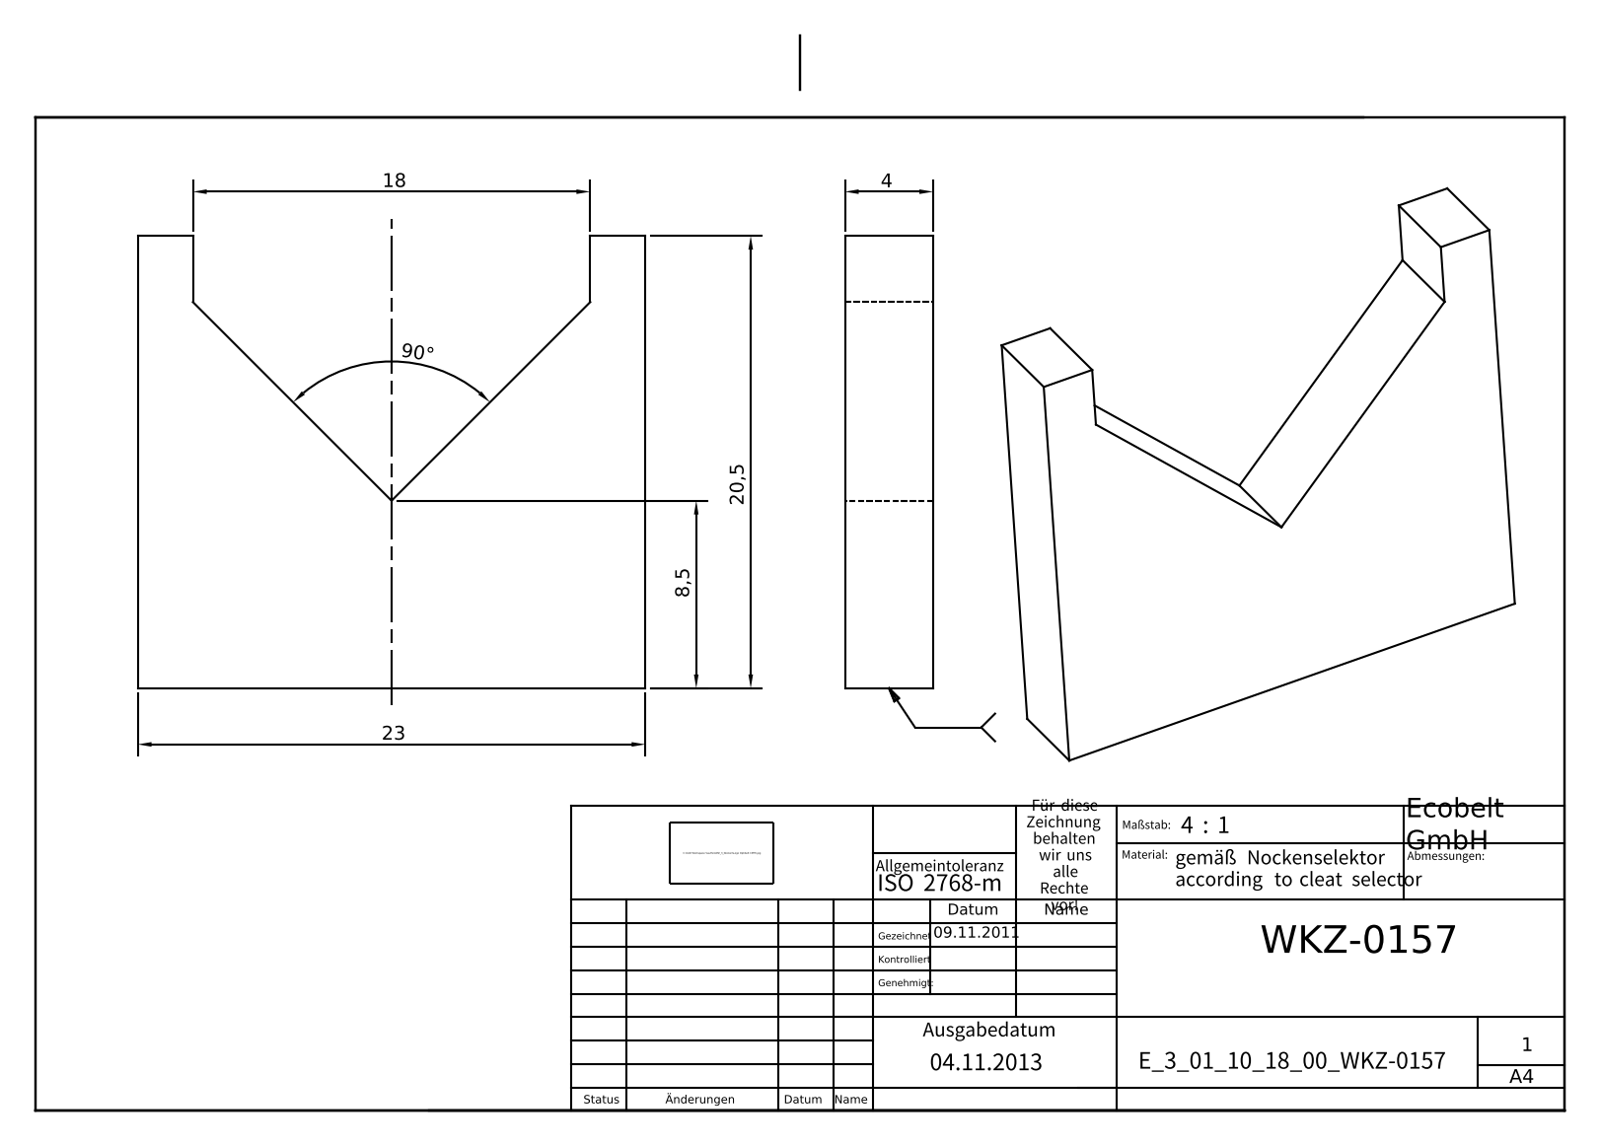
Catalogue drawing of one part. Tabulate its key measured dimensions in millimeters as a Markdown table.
| quantity | value |
| --- | --- |
| part name | E_3_01_10_18_00_WKZ-0157 |
| STEP written by | Autodesk Inventor 2025 (AUTOMOTIVE_DESIGN) |
| units | millimeters |
| bodies | 1 solid, 11 faces (11 planar, 0 cylindrical, 0 other) |
| overall size | 23 × 20.5 × 4 |
| volume | 1 346 mm³ |
| surface area | 1 075 mm² |
| main face-to-face distances | 4, 23, 20.5, 2.5, 18 |
